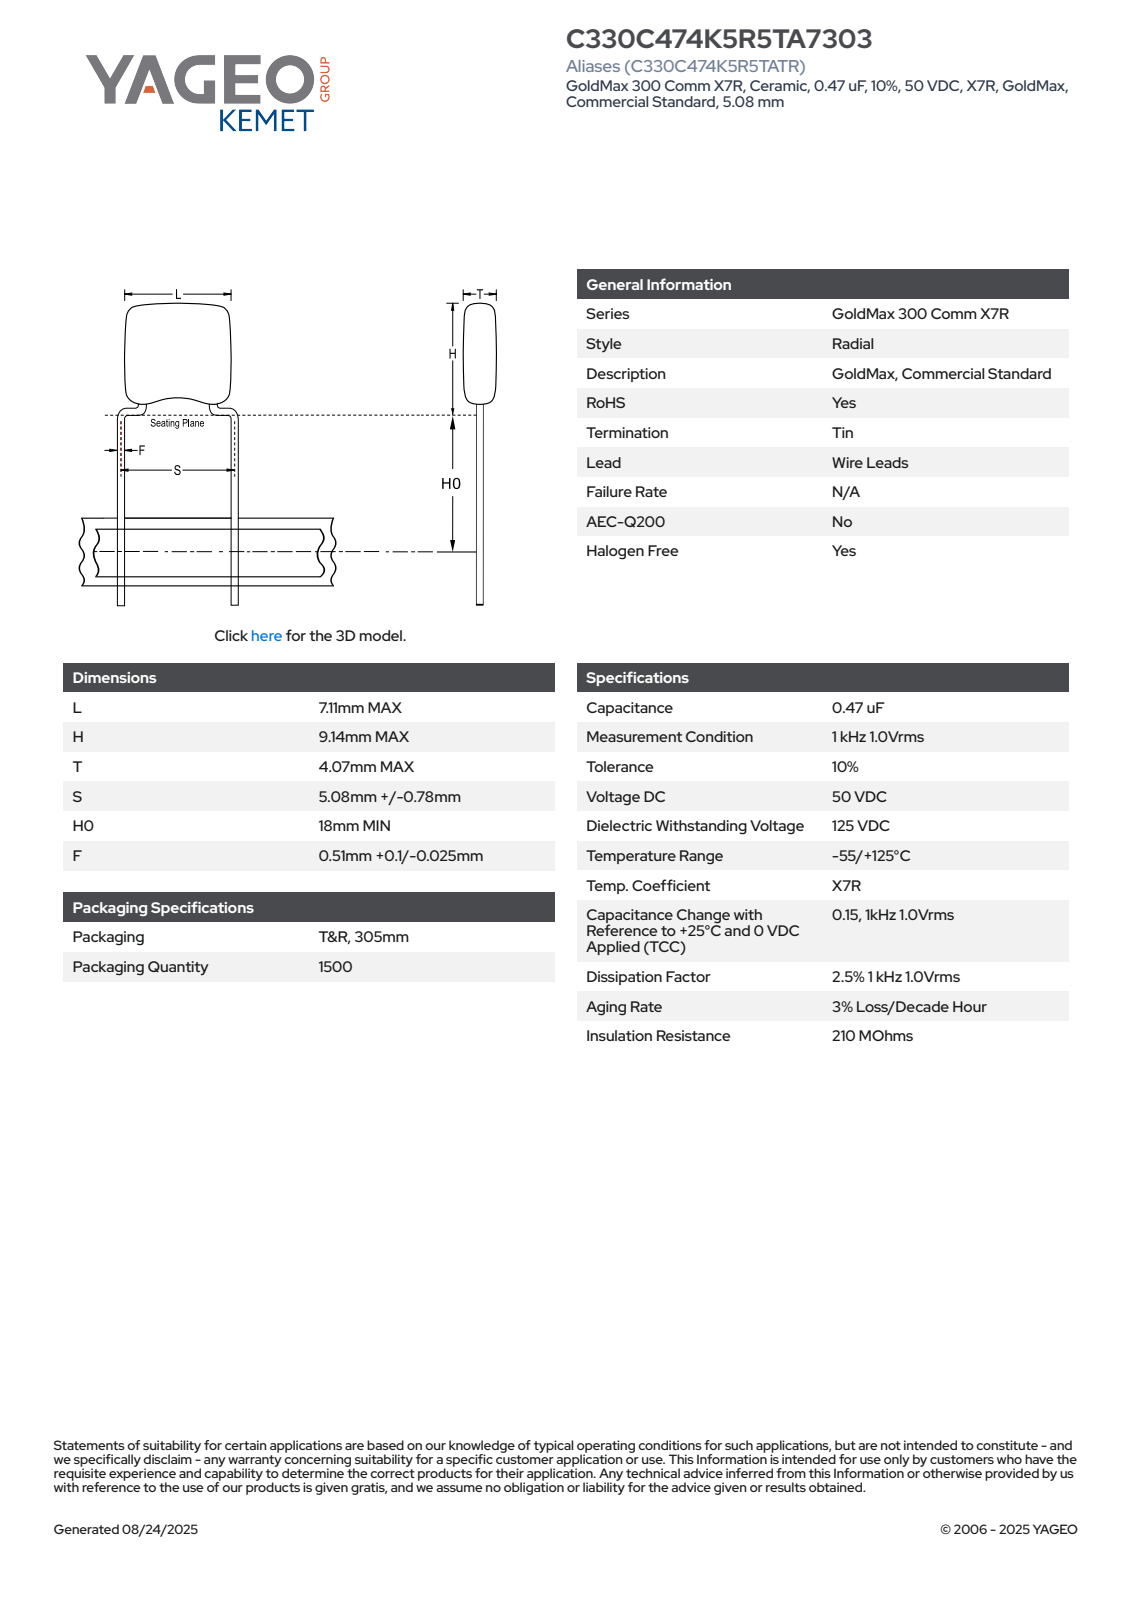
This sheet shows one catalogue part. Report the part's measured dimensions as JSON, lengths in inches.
{"part_name": "CCR_SB_7.11X9.14_L7.11H9.14T4.07S5.08H018F0.51", "step_written_by": "SolidWorks 2014 (AUTOMOTIVE_DESIGN)", "units": "inches", "bodies": {"solids": 4, "faces": 97, "planar": 65, "cylindrical": 14, "other": 18}, "overall_size": [1.069, 0.28, 0.161], "volume_in3": 0.012, "surface_area_in2": 0.388, "round_bosses_or_shafts": [[0.02, 2]], "partial_cylinders_radius": [[0.039, 10]], "face_to_face_distances": [0.16, 0.28, 0.265, 0.161, 0.024, 0.143, 0.122, 0.12, 0.145, 0.13]}
